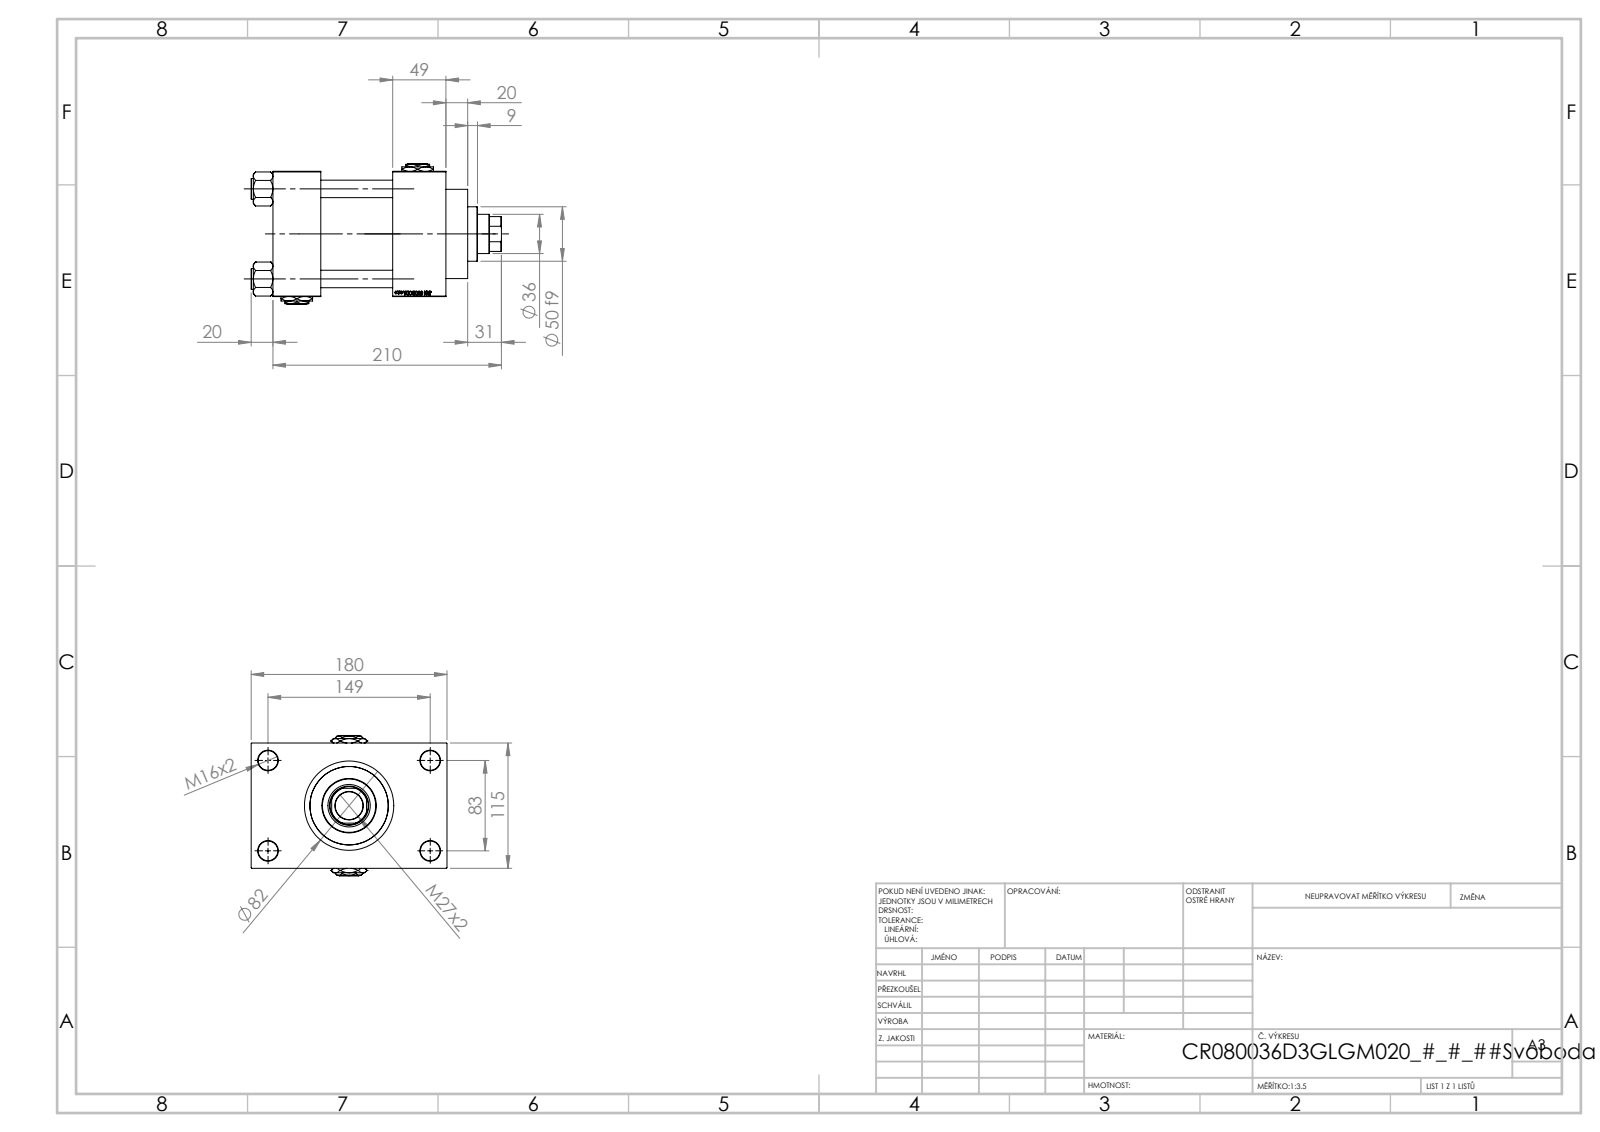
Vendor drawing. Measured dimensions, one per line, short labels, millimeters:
name: V215CR_VCP_D; V215CR_D_Body; Zatka_pro_OIL_PORT; NUT_M5_D (+2 more)
written by: SolidWorks 2019 (CONFIG_CONTROL_DESIGN)
unit: mm
bodies: 13 solids, 1236 faces (589 planar, 89 cylindrical, 558 other)
size: 230 × 180 × 129
volume: 2 005 000 mm³; area: 297 927 mm²
holes: 4× ⌀16, 4× ⌀18, 2× ⌀7, 2× ⌀26.44, 2× ⌀35, 1× ⌀25.5, 1× ⌀36, 1× ⌀39, 1× ⌀61, 1× ⌀72, 1× ⌀80
bosses: 4× ⌀19, 1× ⌀86, 1× ⌀82, 1× ⌀50
rounds: 1× R17.5
face distances: 115, 66, 110, 49, 44, 159, 147.5, 32.5, 20, 69
hole spacings: 33.15, 58.48, 82.7, 85.28, 89.24, 115.85, 142.43, 83
